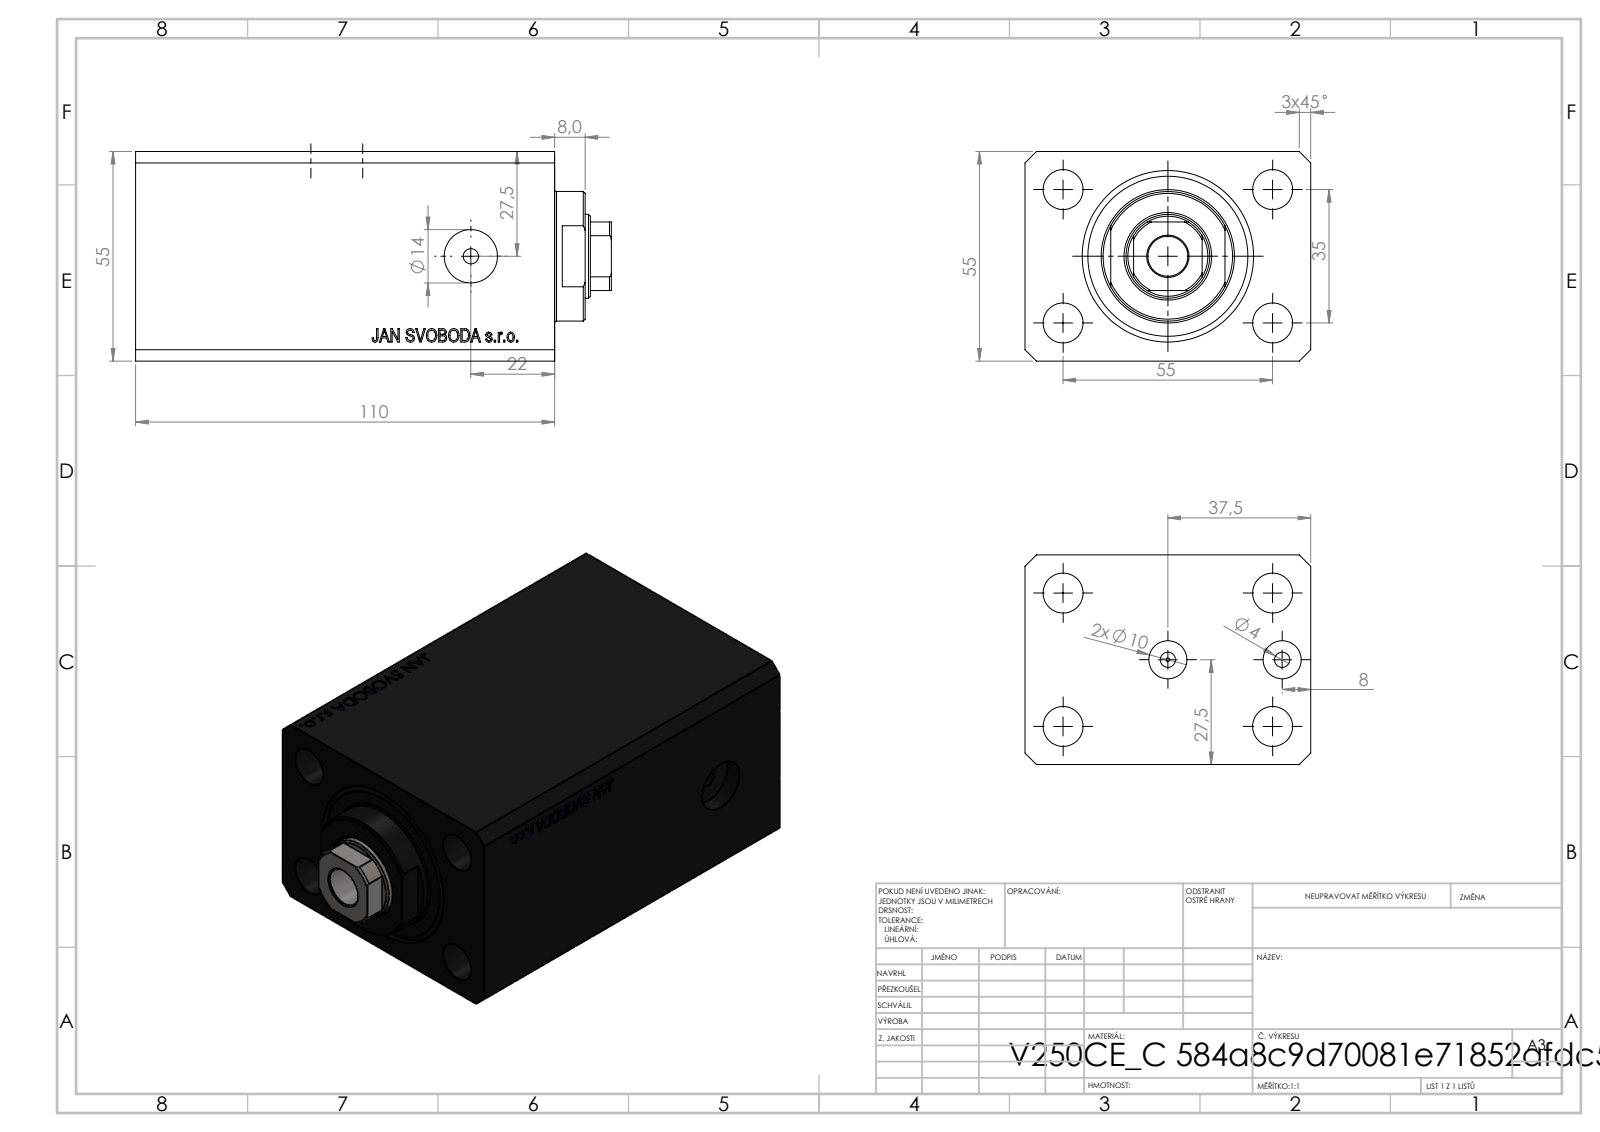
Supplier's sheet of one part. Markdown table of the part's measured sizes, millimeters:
| quantity | value |
| --- | --- |
| part name | V250CE_C_Body; V250CE_VC_C; V250CE_C_VCP |
| STEP written by | SolidWorks 2019 (CONFIG_CONTROL_DESIGN) |
| units | millimeters |
| bodies | 3 solids, 868 faces (428 planar, 46 cylindrical, 394 other) |
| overall size | 124.9 × 75 × 55 |
| volume | 396 266 mm³ |
| surface area | 83 927 mm² |
| round holes (diameter × count) | 10.5 × 5, 4 × 4, 10 × 2, 14 × 2, 1.25 × 1, 22 × 1, 32 × 1, 45 × 1 |
| round bosses / shafts (diameter × count) | 34 × 1 |
| partial cylindrical surfaces (radius × count) | 10.5 × 1 |
| main face-to-face distances | 55, 75, 110, 82.9, 27.1, 73, 9.9, 100.1, 87.66, 8 |
| hole center spacings | 32.6, 17.68, 35, 55, 60.1, 65.19, 30, 66 |
